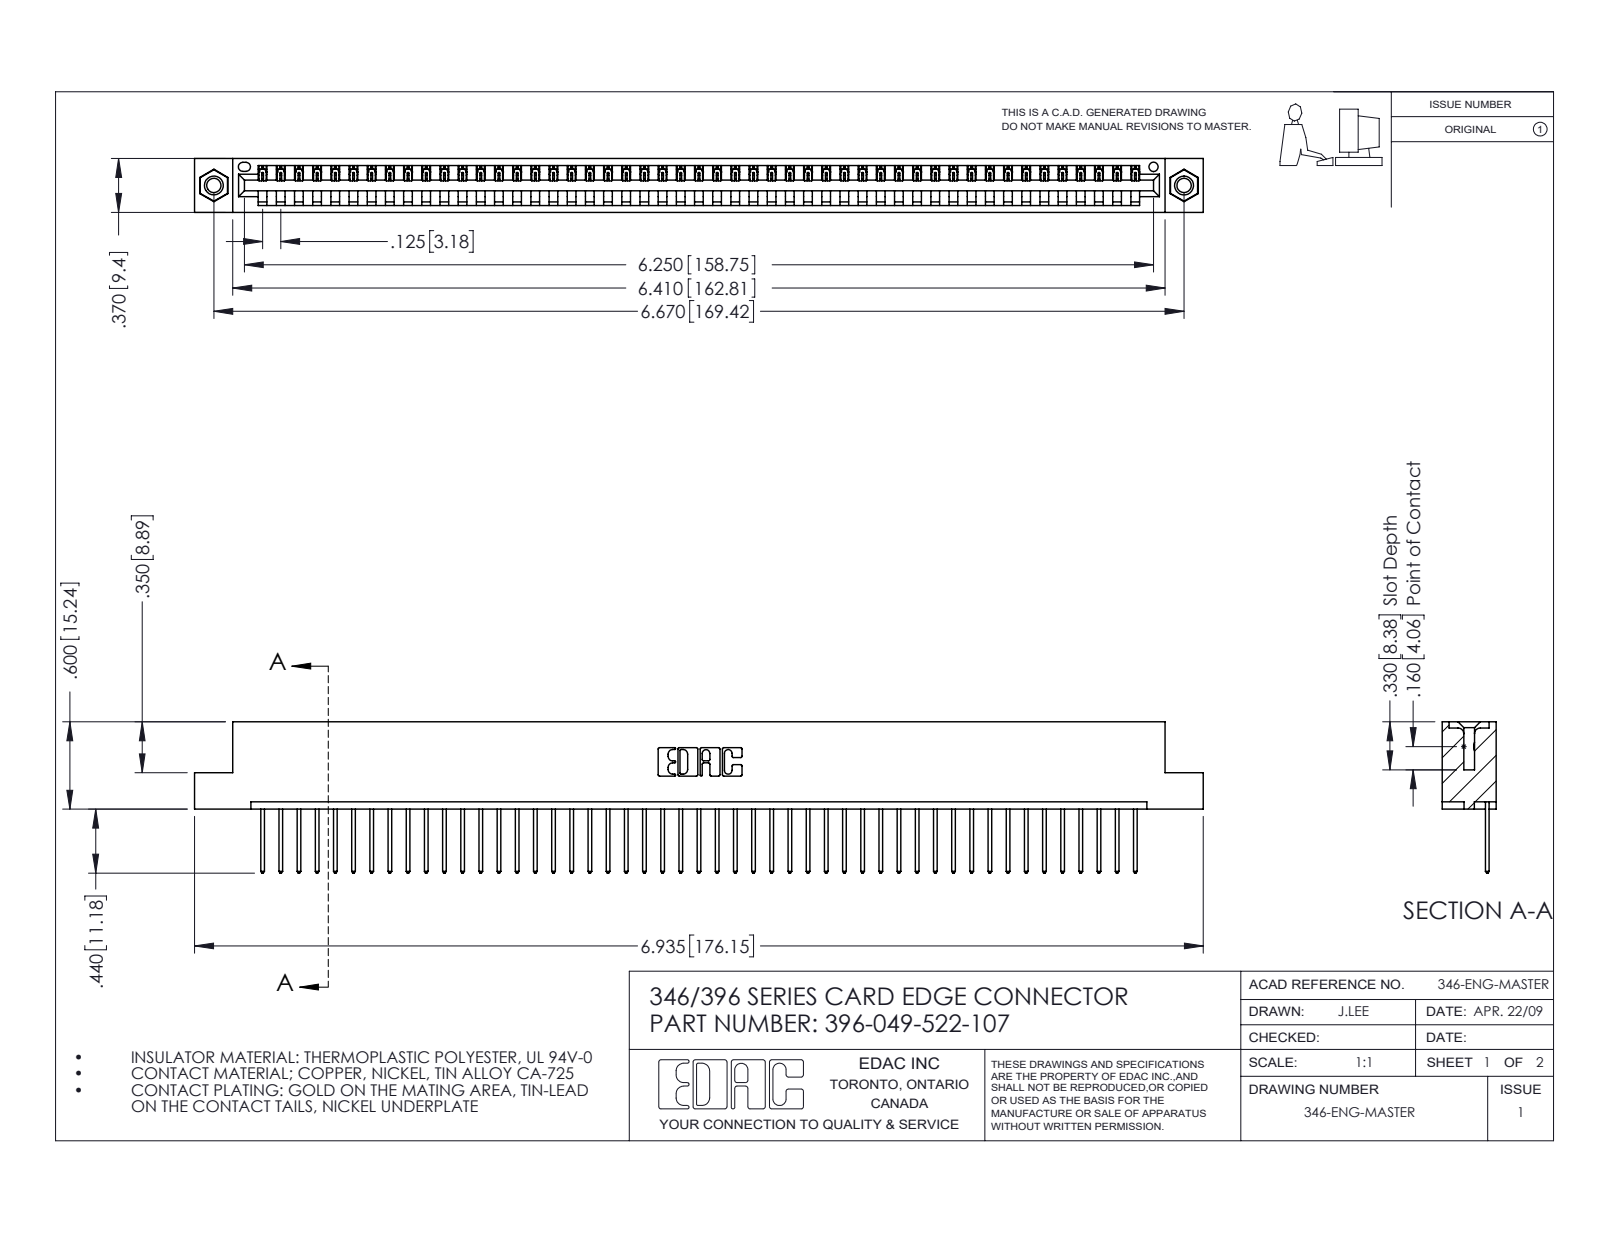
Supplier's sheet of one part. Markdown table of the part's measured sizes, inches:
| quantity | value |
| --- | --- |
| part name | 346 Part_Flush Mounting Lugs - 0.156 Dia-TI; 345-250-001_345-250-005-103; 345-292-001_345-293-122; 396-049-522-107 |
| STEP written by | SolidWorks 2016 (CONFIG_CONTROL_DESIGN) |
| units | inches |
| bodies | 52 solids, 3024 faces (2068 planar, 940 cylindrical, 16 other) |
| overall size | 6.935 × 1.04 × 0.37 |
| volume | 1.031 in³ |
| surface area | 33.2 in² |
| round holes (diameter × count) | 0.098 × 2, 0.125 × 2, 0.156 × 2, 0.064 × 1 |
| round bosses / shafts (diameter × count) | 0.155 × 2 |
| partial cylindrical surfaces (radius × count) | 0.006 × 98, 0.01 × 98, 0.01 × 22, 0.007 × 6, 0.031 × 6, 0.026 × 3, 0.031 × 2, 0.04 × 2 |
| main face-to-face distances | 0.048, 0.322, 0.37, 0.25, 0.072, 0.298, 0.025, 0.148, 0.222, 0.1 |
| hole center spacings | 0.246, 6.461, 6.67 |
